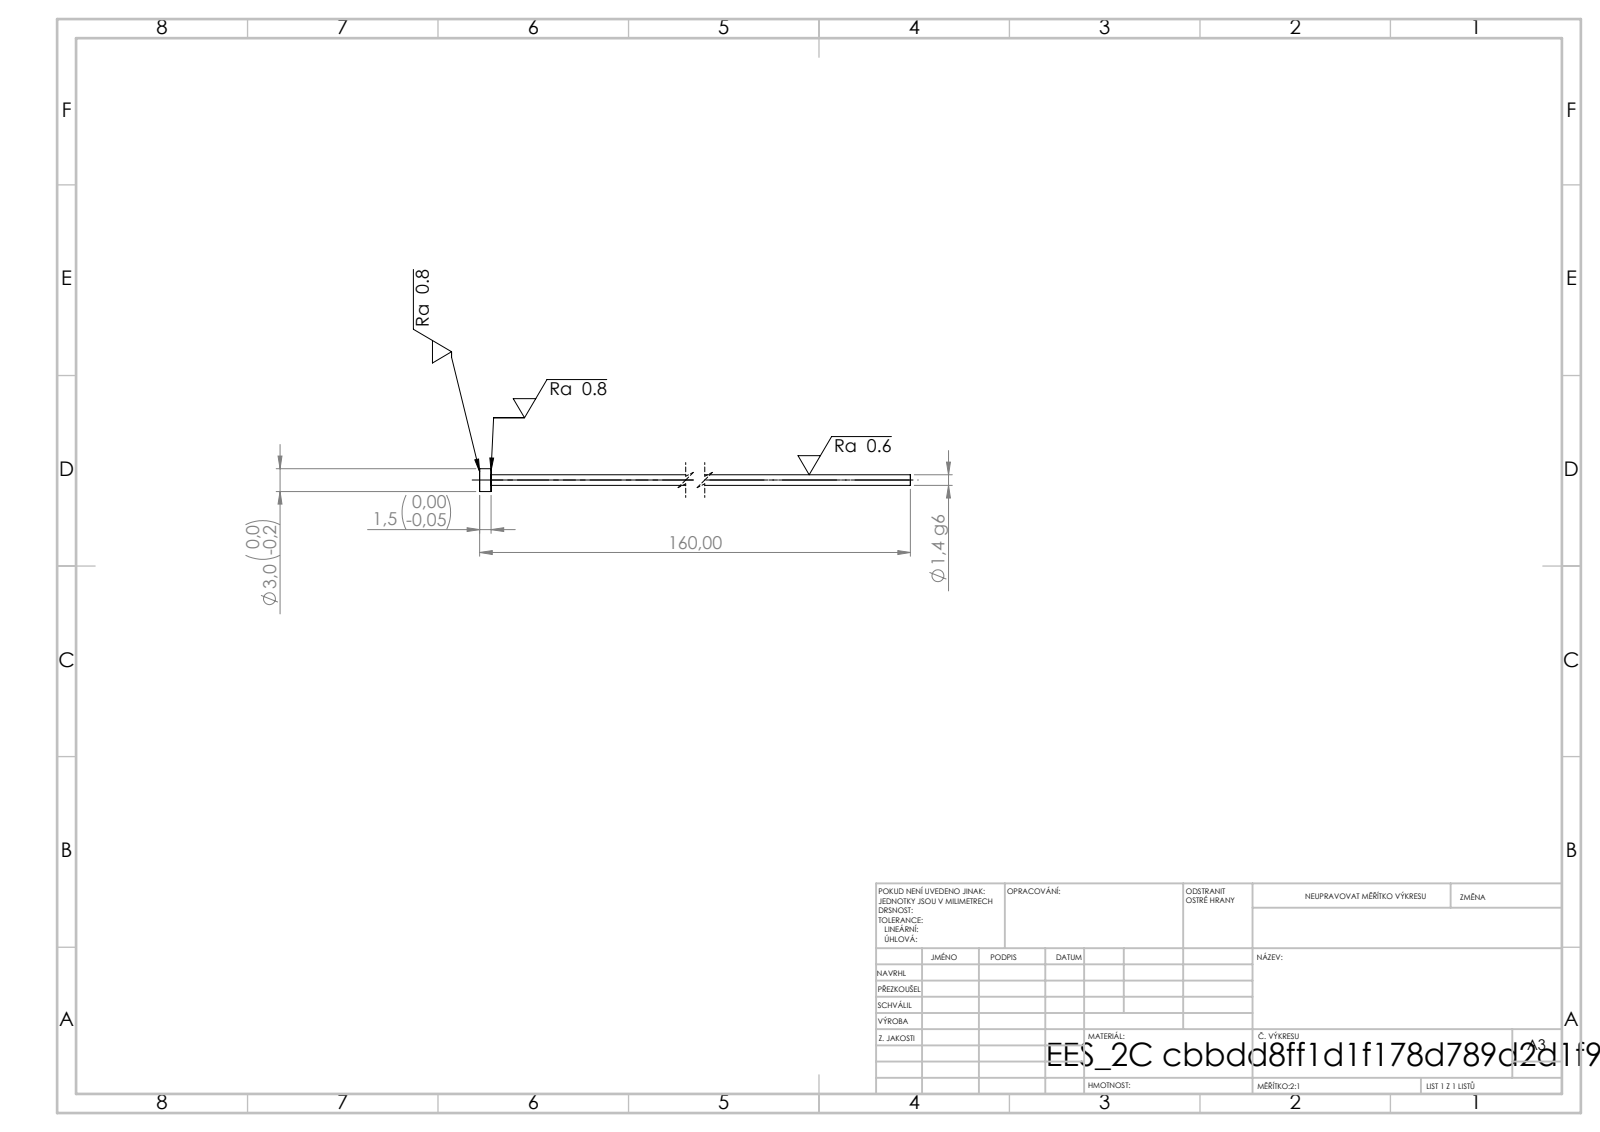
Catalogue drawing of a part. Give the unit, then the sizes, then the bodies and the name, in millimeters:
Units: millimetres
Overall size (bounding box): 160 × 3 × 3
Round bosses / shafts (diameter × count): ⌀3 ×1, ⌀1.4 ×1
Main face-to-face distances: 1.5, 160, 158.5
Volume: 255 mm³ · Surface area: 725 mm²
Bodies: 1 solid, 7 faces (3 planar, 4 cylindrical, 0 other)
STEP written by: SolidWorks 2019 (CONFIG_CONTROL_DESIGN)
